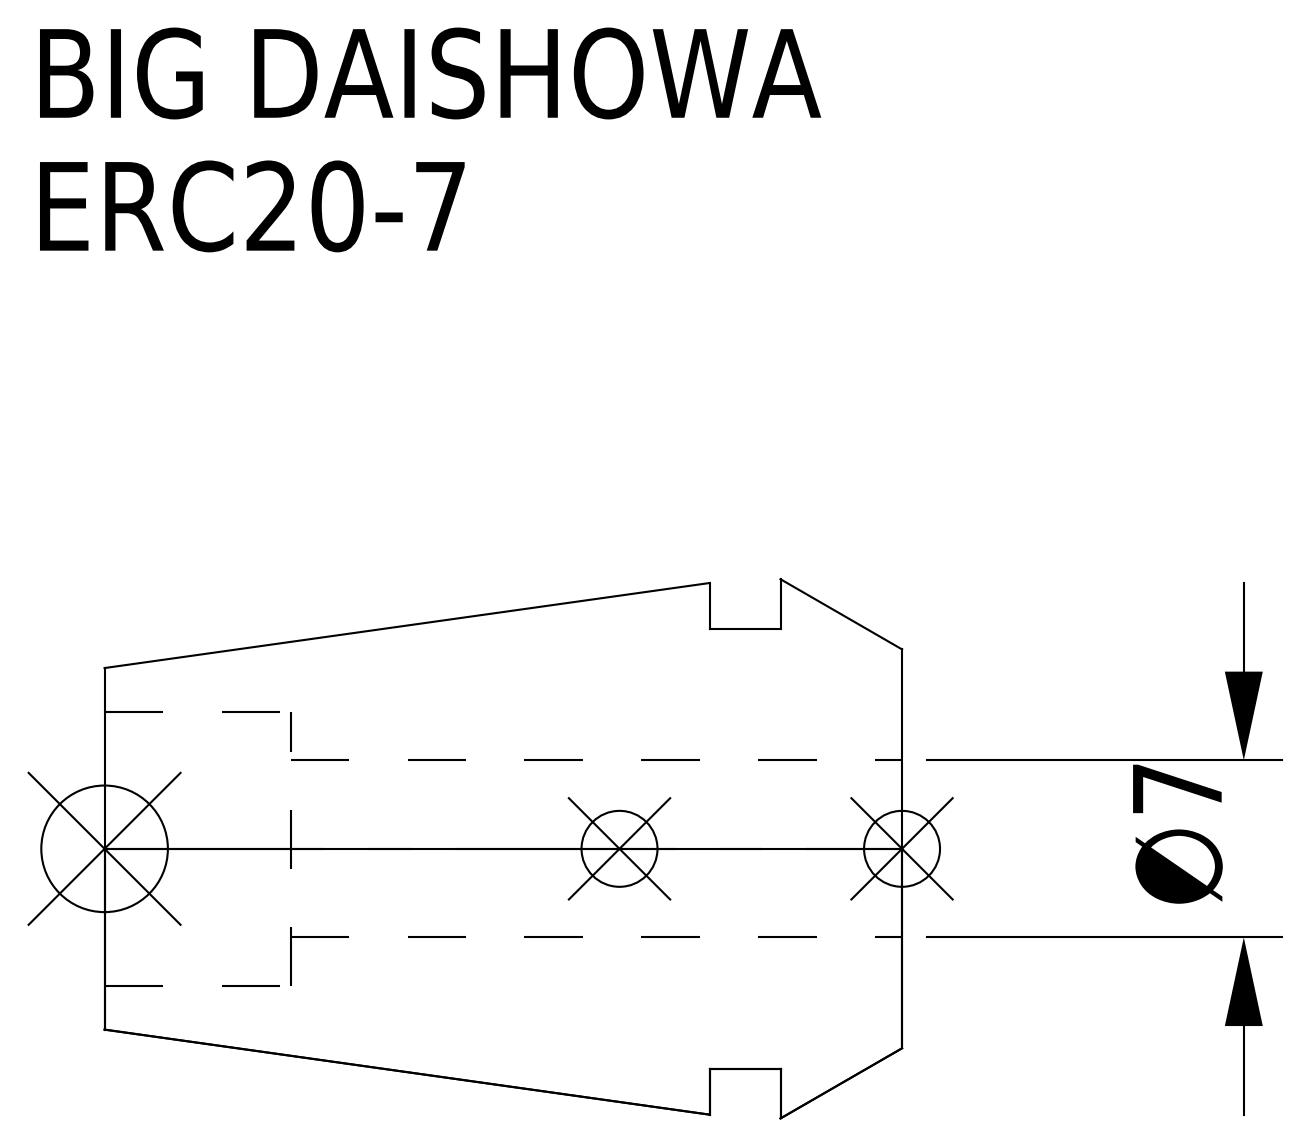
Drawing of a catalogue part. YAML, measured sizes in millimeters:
part_name: "ERC20-7"
step_written_by: "CREO PARAMETRIC BY PTC INC, 2016380 (AUTOMOTIVE_DESIGN)"
units: millimeters
bodies: {solids: 1, faces: 15, planar: 5, cylindrical: 6, other: 4}
overall_size: [31.5, 21.3, 21.3]
volume: 6280
surface_area: 3099
round_holes:
  - {diameter: 7, count: 1}
  - {diameter: 10.8, count: 1}
round_bosses_or_shafts:
  - {diameter: 17.4, count: 1}
face_to_face_distances: [4.8, 7.6, 2.8, 31.5, 26.7, 23.9, 24.16, 19.36, 16.56, 7.34]
